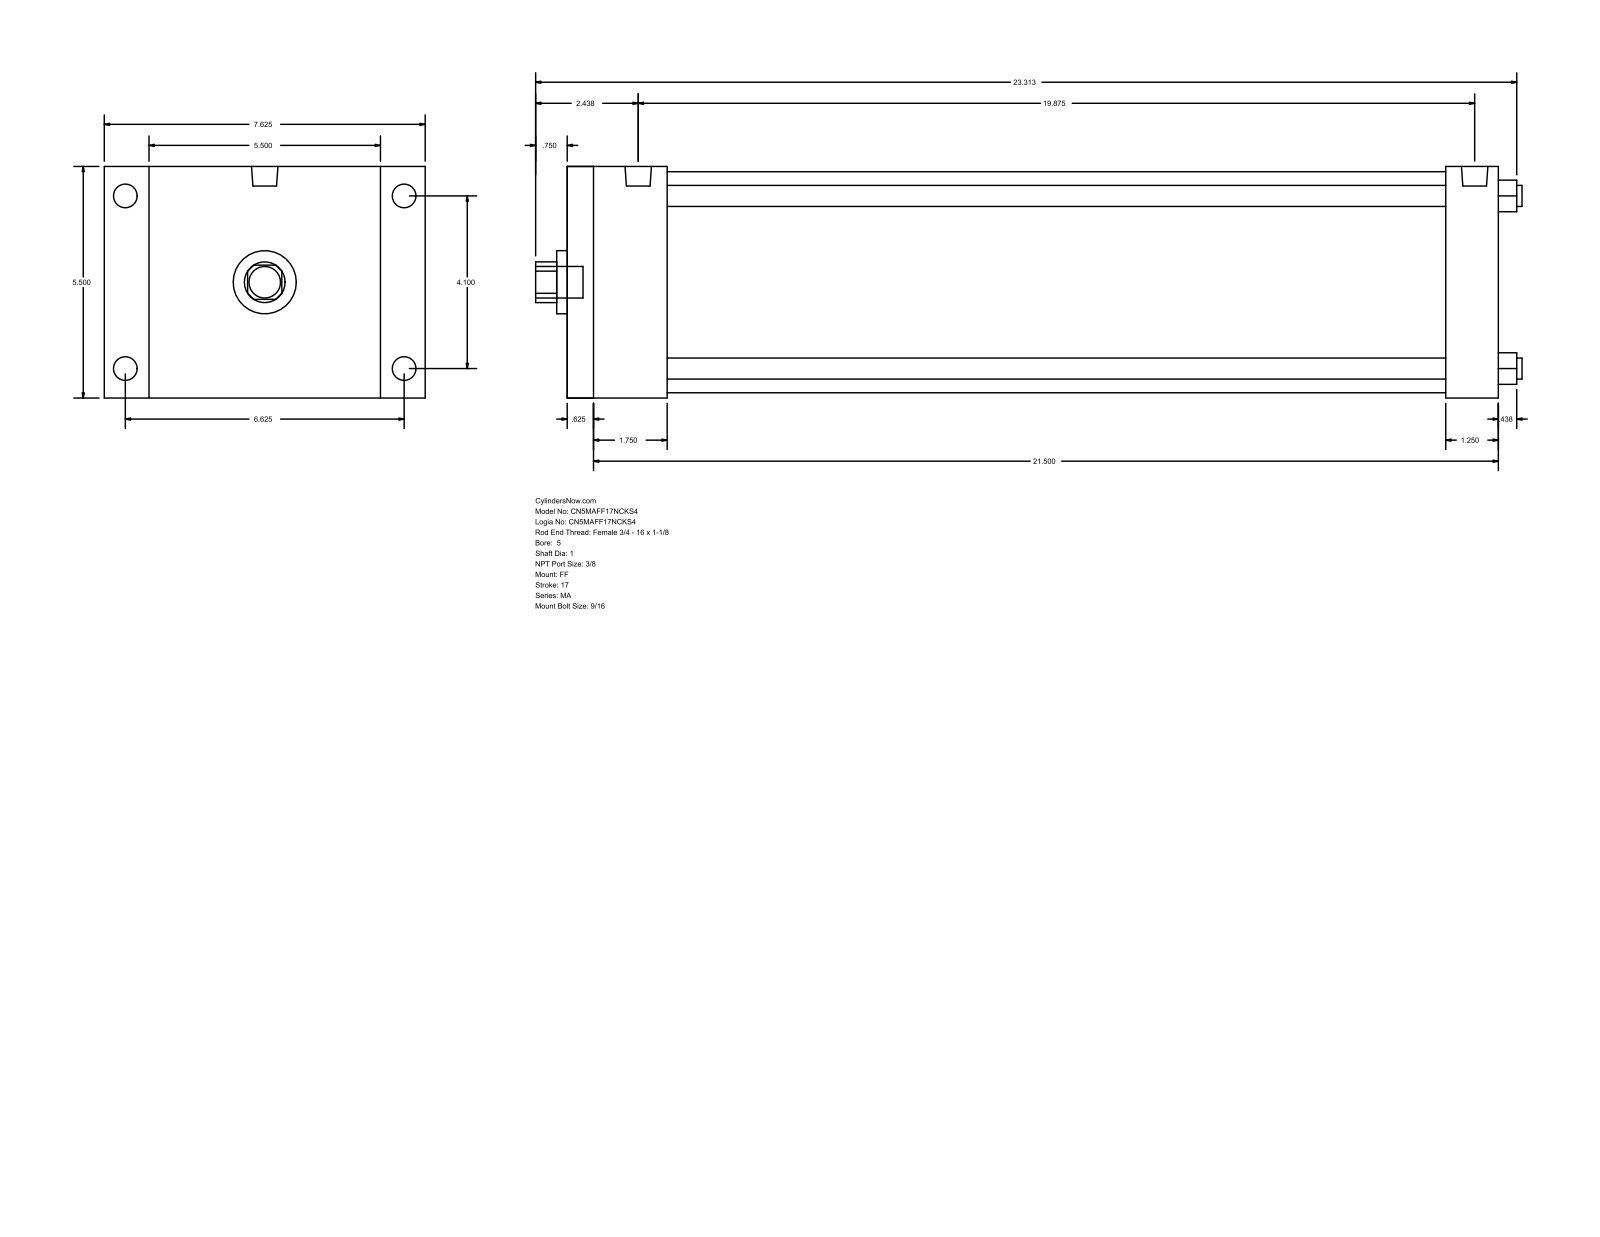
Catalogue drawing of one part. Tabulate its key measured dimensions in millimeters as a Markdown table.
| quantity | value |
| --- | --- |
| part name | MA_FF__0500_1 |
| STEP written by | GSSL Pune (CONFIG_CONTROL_DESIGN) |
| units | millimeters |
| bodies | 0 solids, 92 faces (64 planar, 28 cylindrical, 0 other) |
| overall size | 595.31 × 193.68 × 139.7 |
| round holes (diameter × count) | 12.7 × 4, 25.4 × 1, 38.1 × 1, 133.35 × 1 |
| round bosses / shafts (diameter × count) | 14.29 × 4, 11.11 × 4, 15.93 × 2, 19.05 × 1 |
| partial cylindrical surfaces (radius × count) | 12.29 × 1 |
| main face-to-face distances | 139.7, 561.97, 15.87, 546.1, 530.22, 514.35, 31.75, 60.33, 44.46, 469.89 |
| hole center spacings | 73.64, 104.14, 147.28 |
